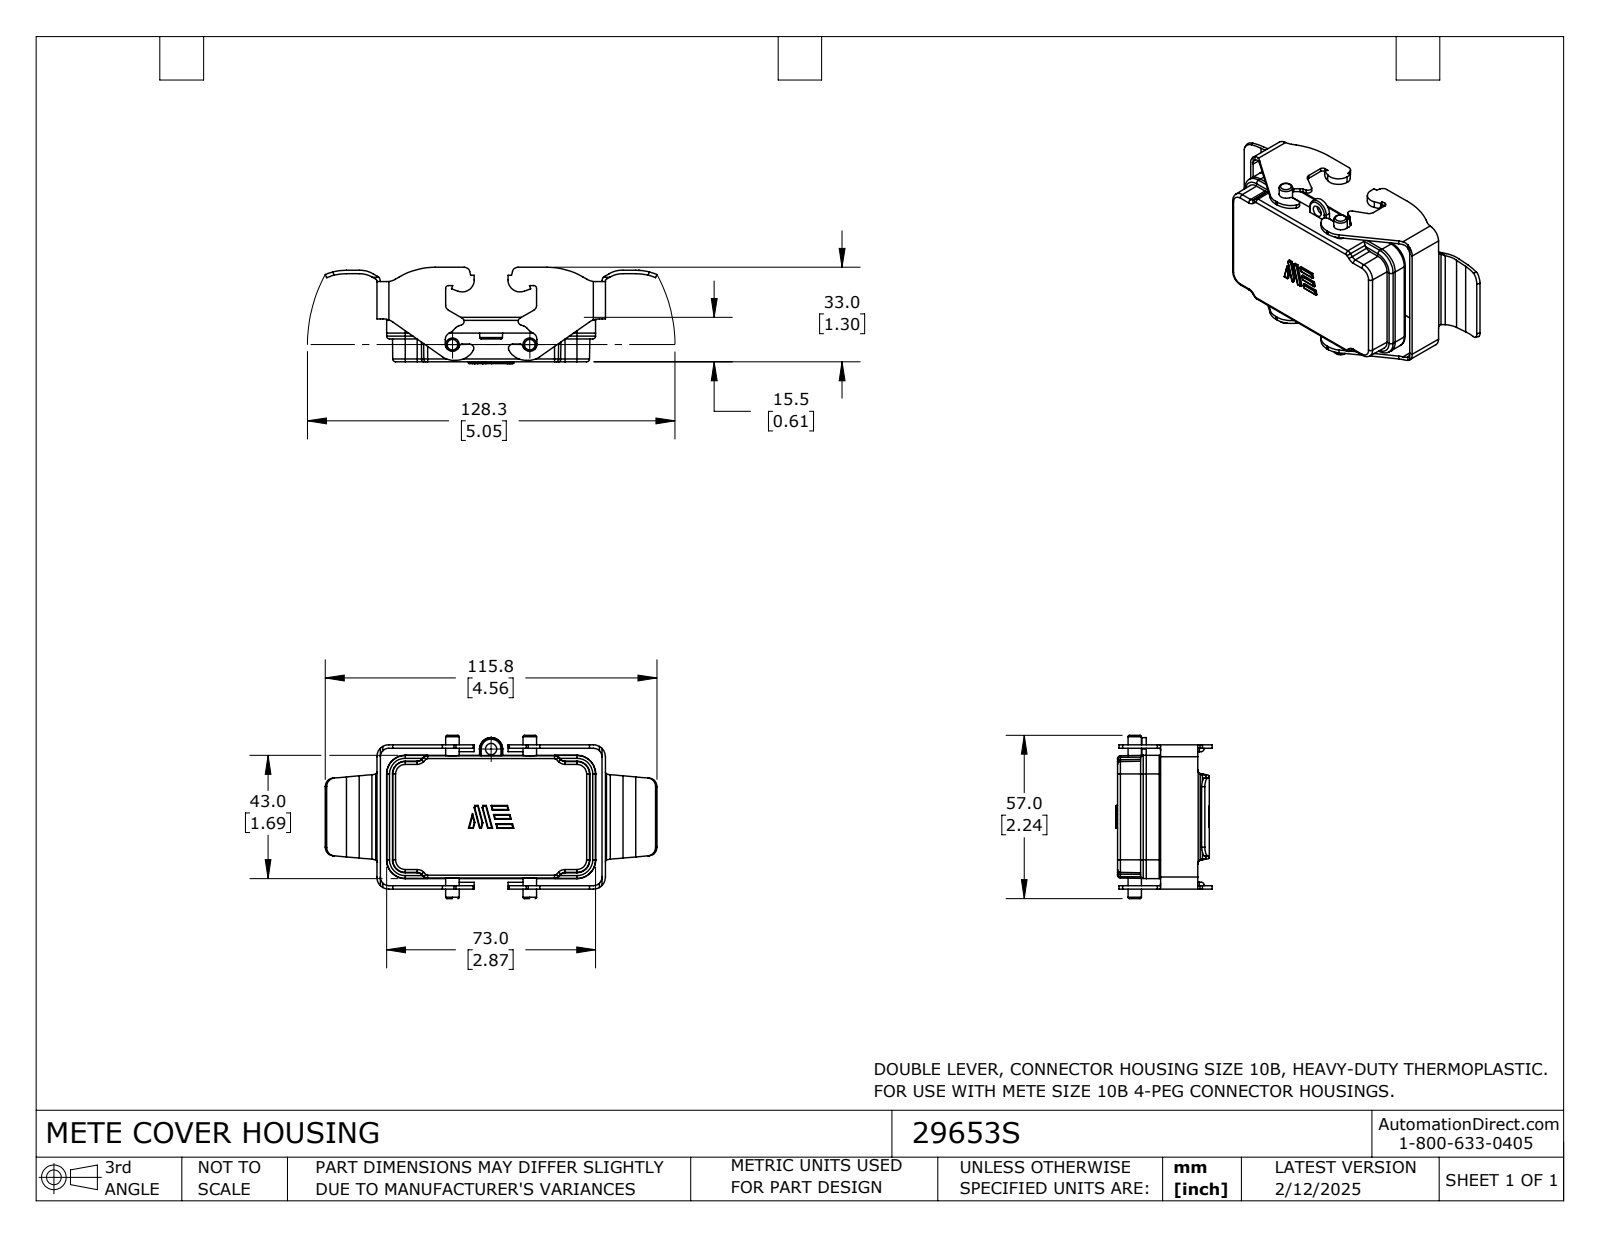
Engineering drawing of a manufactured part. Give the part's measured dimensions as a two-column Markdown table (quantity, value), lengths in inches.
| quantity | value |
| --- | --- |
| part name | 29653S |
| STEP written by | SolidWorks 2024 (CONFIG_CONTROL_DESIGN) |
| units | inches |
| bodies | 1 solid, 533 faces (206 planar, 243 cylindrical, 84 other) |
| overall size | 4.559 × 2.244 × 1.323 |
| volume | 1.24 in³ |
| surface area | 36.39 in² |
| round bosses / shafts (diameter × count) | 0.185 × 2 |
| partial cylindrical surfaces (radius × count) | 0.008 × 50, 0.039 × 32, 0.02 × 14, 0.118 × 10, 0.059 × 6, 0.079 × 6, 0.098 × 6, 0.165 × 6 |
| main face-to-face distances | 0.047, 0.079, 1.937, 0.146, 1.89, 1.984, 3.094, 1.693, 0.102, 0.244 |
